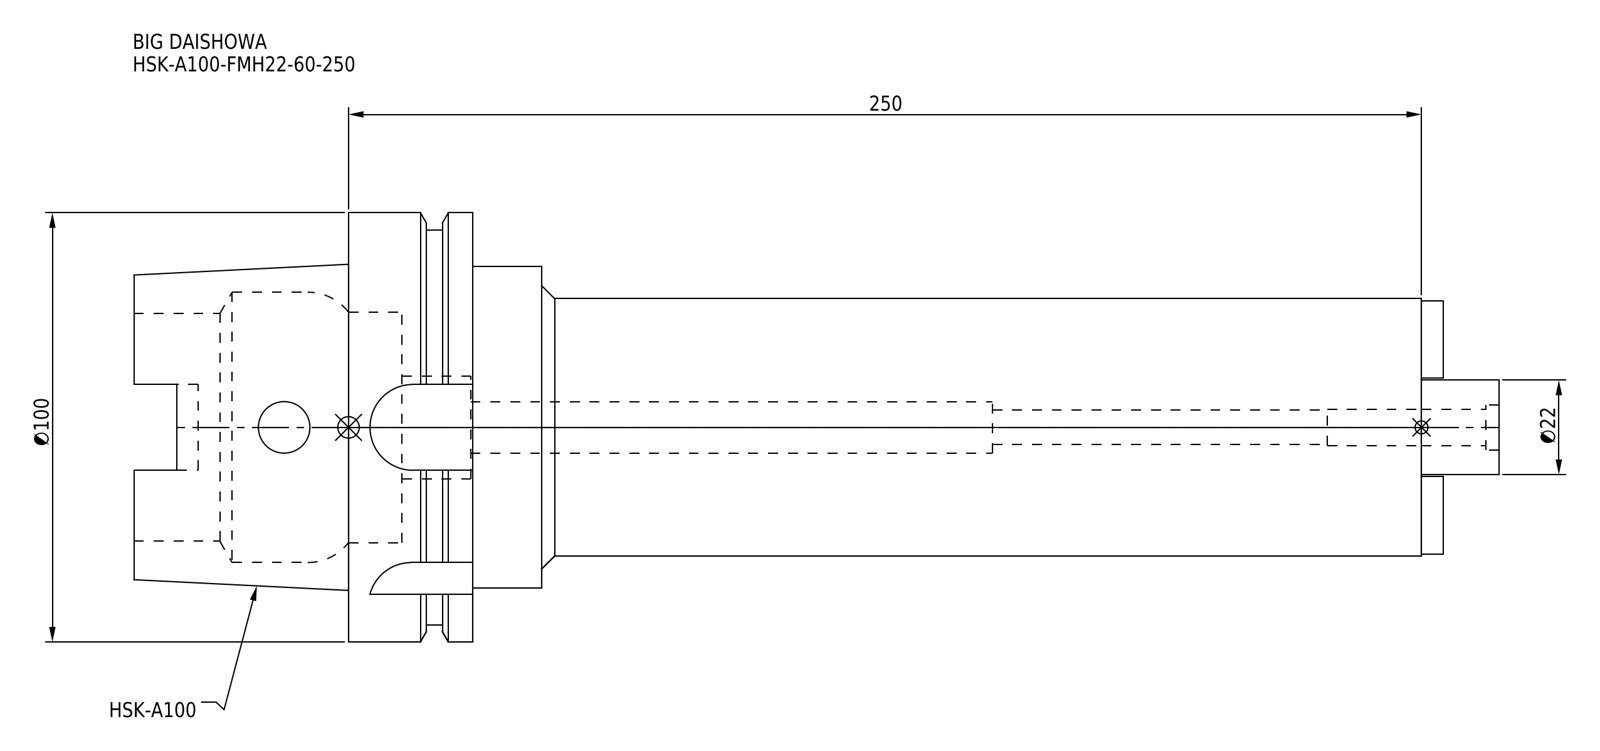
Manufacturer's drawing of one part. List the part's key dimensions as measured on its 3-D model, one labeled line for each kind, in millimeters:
Part name (STEP PRODUCT): HSK-A100-FMH22-60-250
STEP written by: CREO PARAMETRIC BY PTC INC, 2016380 (AUTOMOTIVE_DESIGN)
Units: millimetres
Bodies: 1 solid, 109 faces (47 planar, 46 cylindrical, 16 other)
Overall size (bounding box): 318 × 100 × 100
Volume: 893 306 mm³ · Surface area: 101 420 mm²
Round holes (diameter × count): ⌀12 ×2, ⌀8 ×1, ⌀8.5 ×1, ⌀10.5 ×1, ⌀24 ×1, ⌀53 ×1, ⌀53.8 ×1, ⌀63 ×1
Round bosses / shafts (diameter × count): ⌀100 ×1, ⌀92 ×1, ⌀75 ×1, ⌀60 ×1, ⌀22 ×1
Partial cylindrical surfaces — rounded edges, fillets, slot ends (radius × count): R4.88 ×4, R10 ×4
Main face-to-face distances: 29, 16.55, 250, 221, 237.55, 12.45, 16, 300, 79, 62.45
